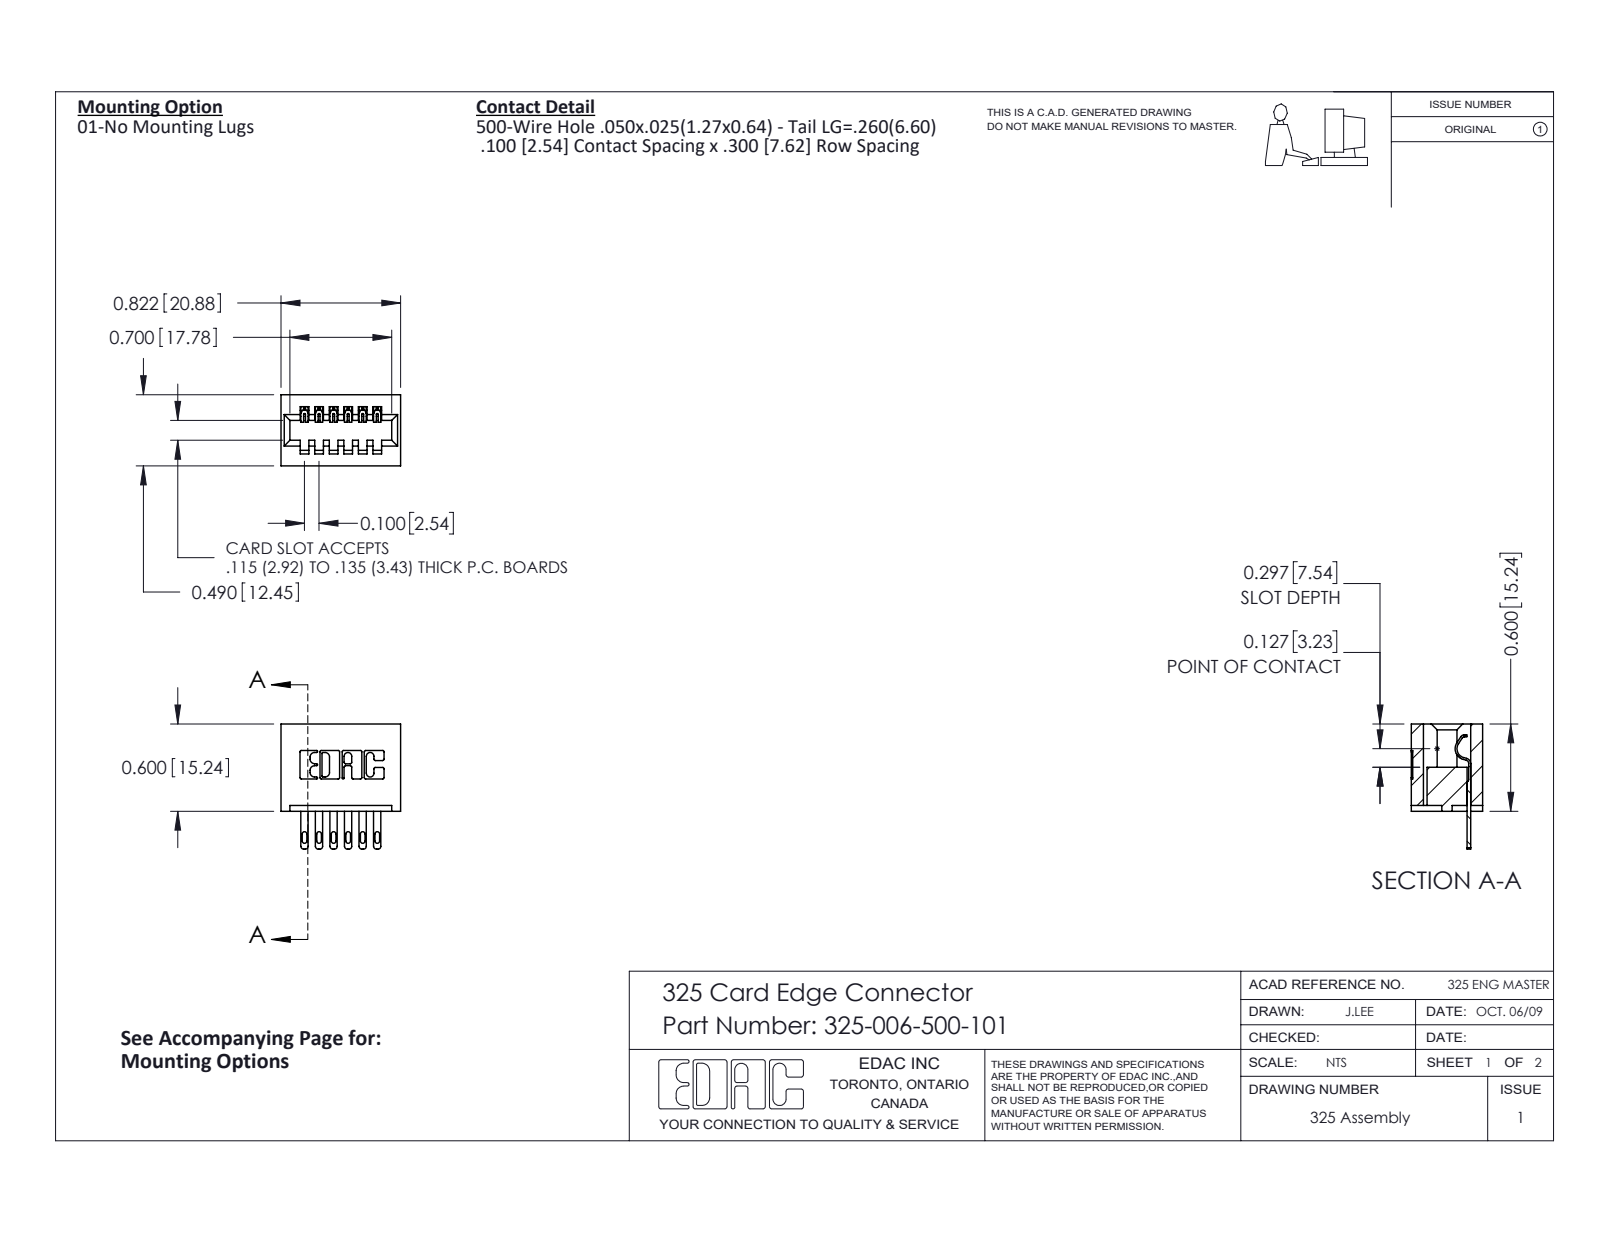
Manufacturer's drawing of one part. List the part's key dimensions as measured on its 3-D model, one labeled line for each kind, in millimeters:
Part name (STEP PRODUCT): 325 Part_Lugless; 325-292-001_325-293-100; 325-006-500-101
STEP written by: SolidWorks 2016 (CONFIG_CONTROL_DESIGN)
Units: millimetres
Bodies: 7 solids, 430 faces (282 planar, 148 cylindrical, 0 other)
Overall size (bounding box): 21.8 × 20.9 × 12.4
Volume: 2 950 mm³ · Surface area: 3 109 mm²
Partial cylindrical surfaces — rounded edges, fillets, slot ends (radius × count): R0.3 ×22, R0.2 ×12, R0.4 ×12, R0.5 ×12, R0.2 ×6, R0.8 ×6, R0.7 ×3, R0.4 ×1
Main face-to-face distances: 7.6, 2.5, 5.1, 2.1, 10.3, 1, 1.5, 12.4, 4.1, 2.7
